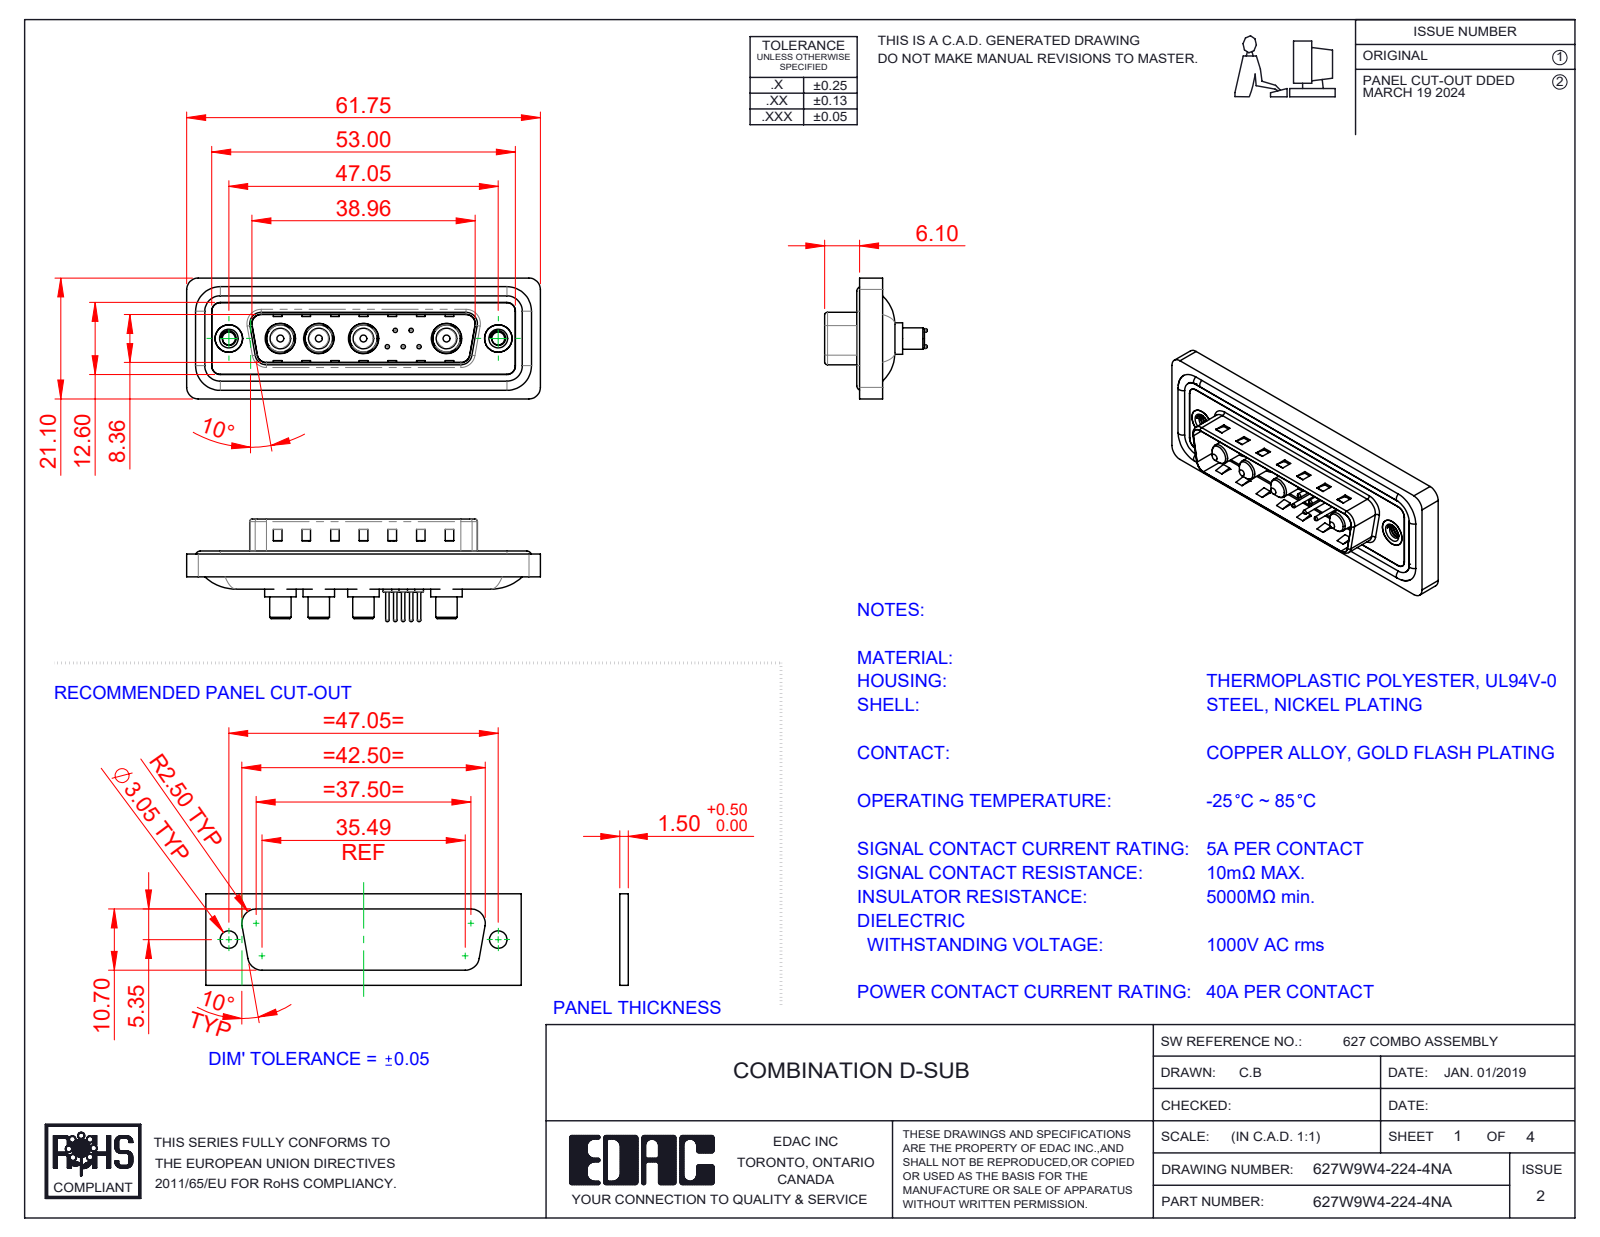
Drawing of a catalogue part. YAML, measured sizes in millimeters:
part_name: "627W9W4-224-4NA; 627Combo Waterproof Housing_25 Contacts; 627Combo Shell Rear_25 Contacts; 627Combo Shell Front_25 Contacts (+5 more)"
step_written_by: "SolidWorks 2023 (CONFIG_CONTROL_DESIGN)"
units: millimeters
bodies: {solids: 20, faces: 822, planar: 284, cylindrical: 336, other: 202}
overall_size: [61.75, 21.1, 17.9]
volume: 7480
surface_area: 11877
round_holes:
  - {diameter: 0.75, count: 5}
  - {diameter: 1.6, count: 5}
  - {diameter: 2, count: 5}
  - {diameter: 4.85, count: 4}
  - {diameter: 5.3, count: 4}
  - {diameter: 2.26, count: 2}
  - {diameter: 4, count: 2}
  - {diameter: 4.8, count: 2}
  - {diameter: 5, count: 2}
round_bosses_or_shafts:
  - {diameter: 1.5, count: 5}
  - {diameter: 0.6, count: 5}
  - {diameter: 5.5, count: 4}
  - {diameter: 5.2, count: 4}
  - {diameter: 4.75, count: 4}
  - {diameter: 3.75, count: 4}
  - {diameter: 3.6, count: 4}
  - {diameter: 1.6, count: 4}
partial_cylinders:
  - {radius: 1.5, count: 22}
  - {radius: 2, count: 18}
  - {radius: 0.5, count: 8}
  - {radius: 1.6, count: 8}
  - {radius: 0.25, count: 4}
  - {radius: 0.6, count: 4}
  - {radius: 0.65, count: 4}
  - {radius: 0.9, count: 4}
face_to_face_distances: [0.4, 1.5, 1.1, 0.5, 1.6, 3.1, 2.9, 0.82, 9.58, 5.65]
hole_center_spacings: [3.16, 2.77, 5.04, 14.51, 2.78, 4.4, 4.41, 5]
